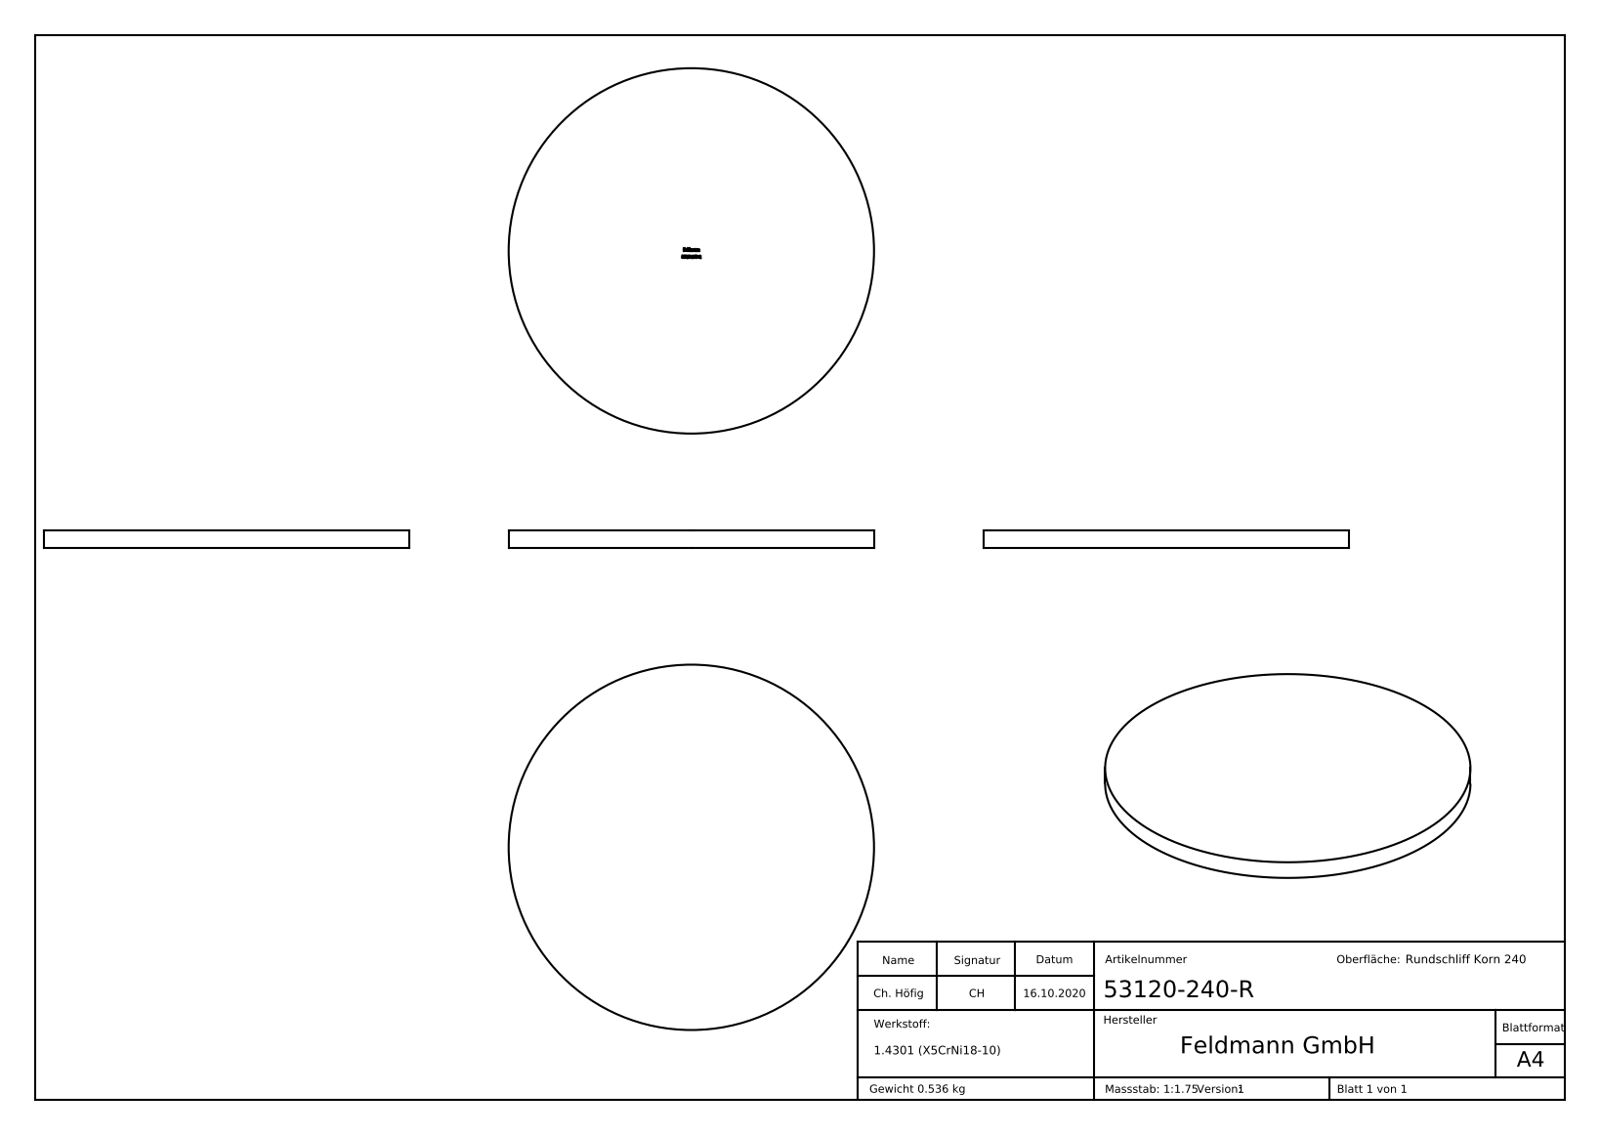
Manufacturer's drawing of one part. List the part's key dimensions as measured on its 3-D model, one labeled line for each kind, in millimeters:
Part name (STEP PRODUCT): 53120-240-R
STEP written by: SolidWorks 2018 (CONFIG_CONTROL_DESIGN)
Units: millimetres
Bodies: 1 solid, 248 faces (141 planar, 2 cylindrical, 105 other)
Overall size (bounding box): 120 × 120 × 6
Volume: 67 858 mm³ · Surface area: 24 888 mm²
Round bosses / shafts (diameter × count): ⌀120 ×1
Main face-to-face distances: 6, 5.9, 1.21, 1.28, 0.79, 0.99, 3.86, 0.92, 2.94, 1.78
